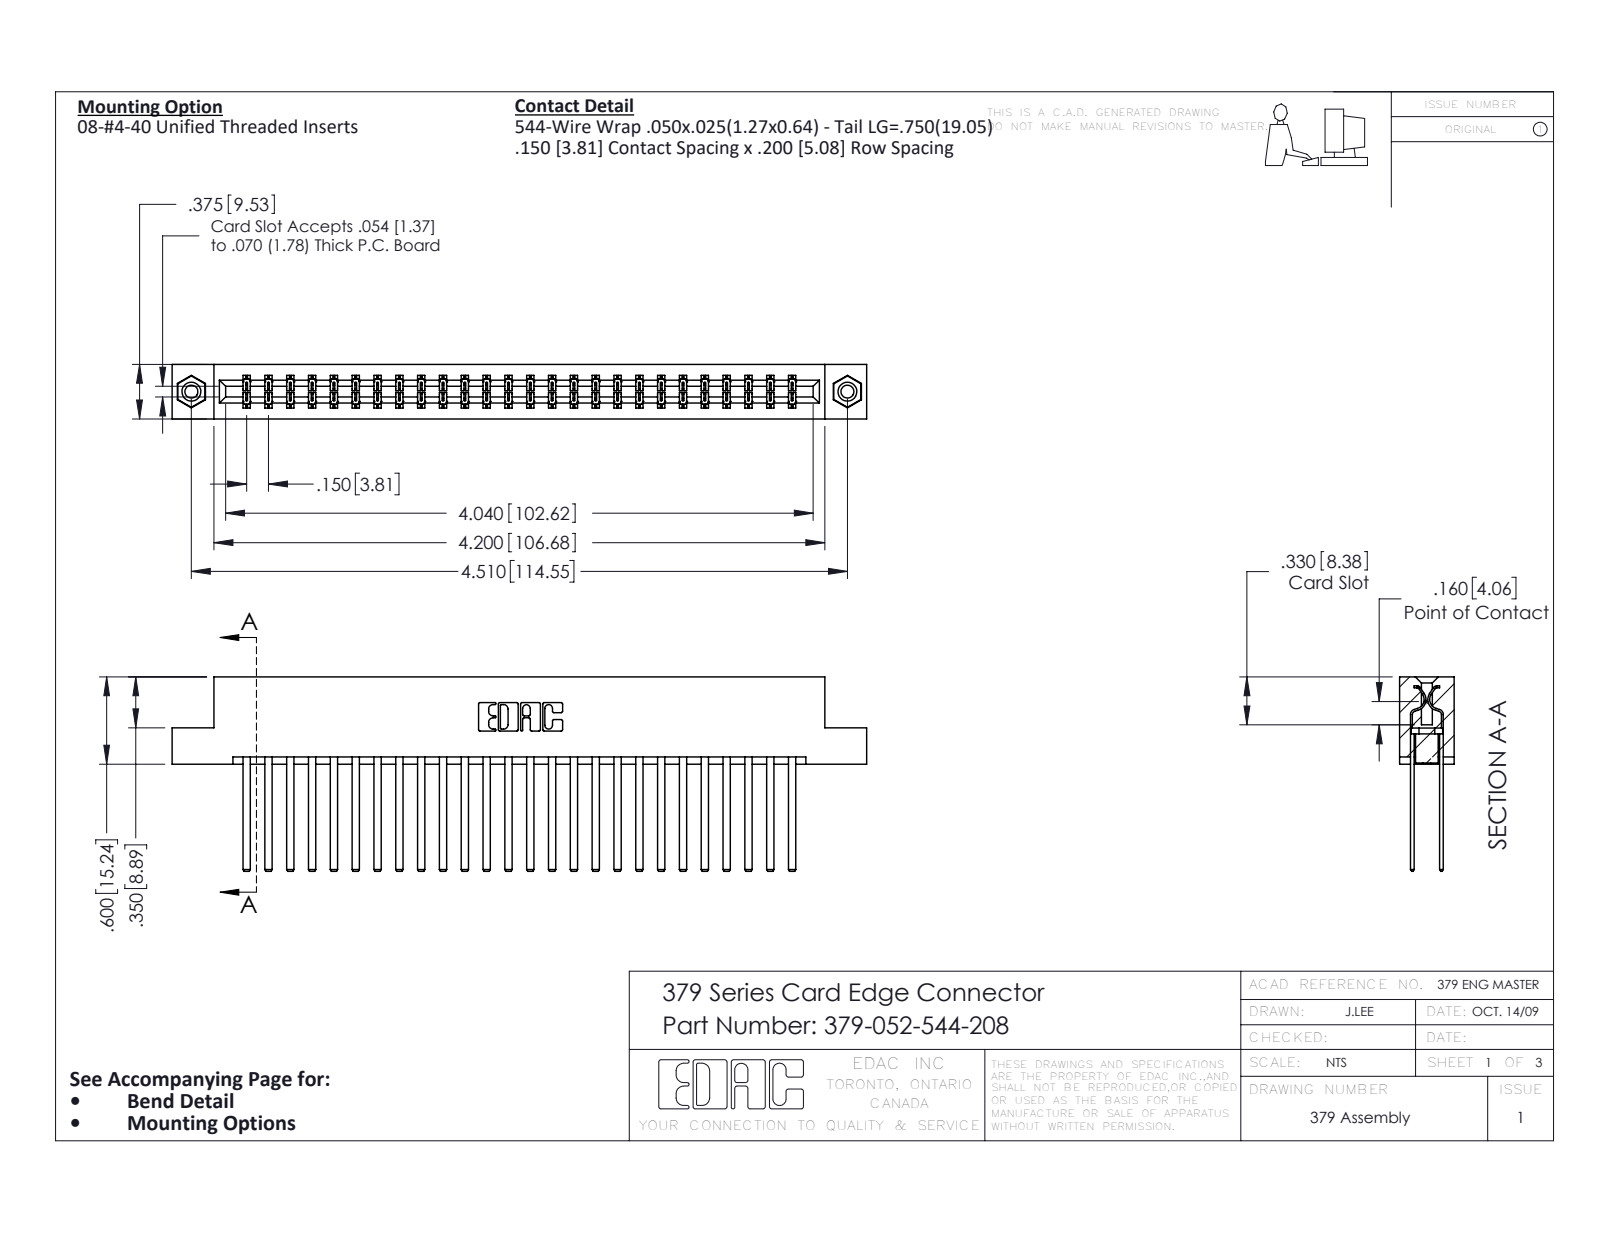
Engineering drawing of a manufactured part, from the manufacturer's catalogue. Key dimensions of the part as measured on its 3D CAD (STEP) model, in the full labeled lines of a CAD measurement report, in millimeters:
Part name (STEP PRODUCT): 379-052-544-208; 345-250-001_345-250-003-102; 379 Part_Flush - .156 Dia - TI; 345-292-001_345-293-144
STEP written by: SolidWorks 2016 (CONFIG_CONTROL_DESIGN)
Units: millimetres
Bodies: 55 solids, 2566 faces (1766 planar, 784 cylindrical, 16 other)
Overall size (bounding box): 121.3 × 34 × 9.5
Volume: 13 400 mm³ · Surface area: 17 370 mm²
Round holes (diameter × count): ⌀2.3 ×2, ⌀3.2 ×2, ⌀4 ×2
Round bosses / shafts (diameter × count): ⌀3.9 ×2
Partial cylindrical surfaces — rounded edges, fillets, slot ends (radius × count): R0.2 ×78, R0.3 ×22, R0.2 ×6, R0.8 ×6, R0.7 ×3, R0.4 ×2, R0.6 ×2, R0.6 ×2
Main face-to-face distances: 7.6, 2.5, 1.9, 5.1, 7, 9.5, 0.6, 3.8, 15.2, 1.9
Hole centre spacings: 114.6
